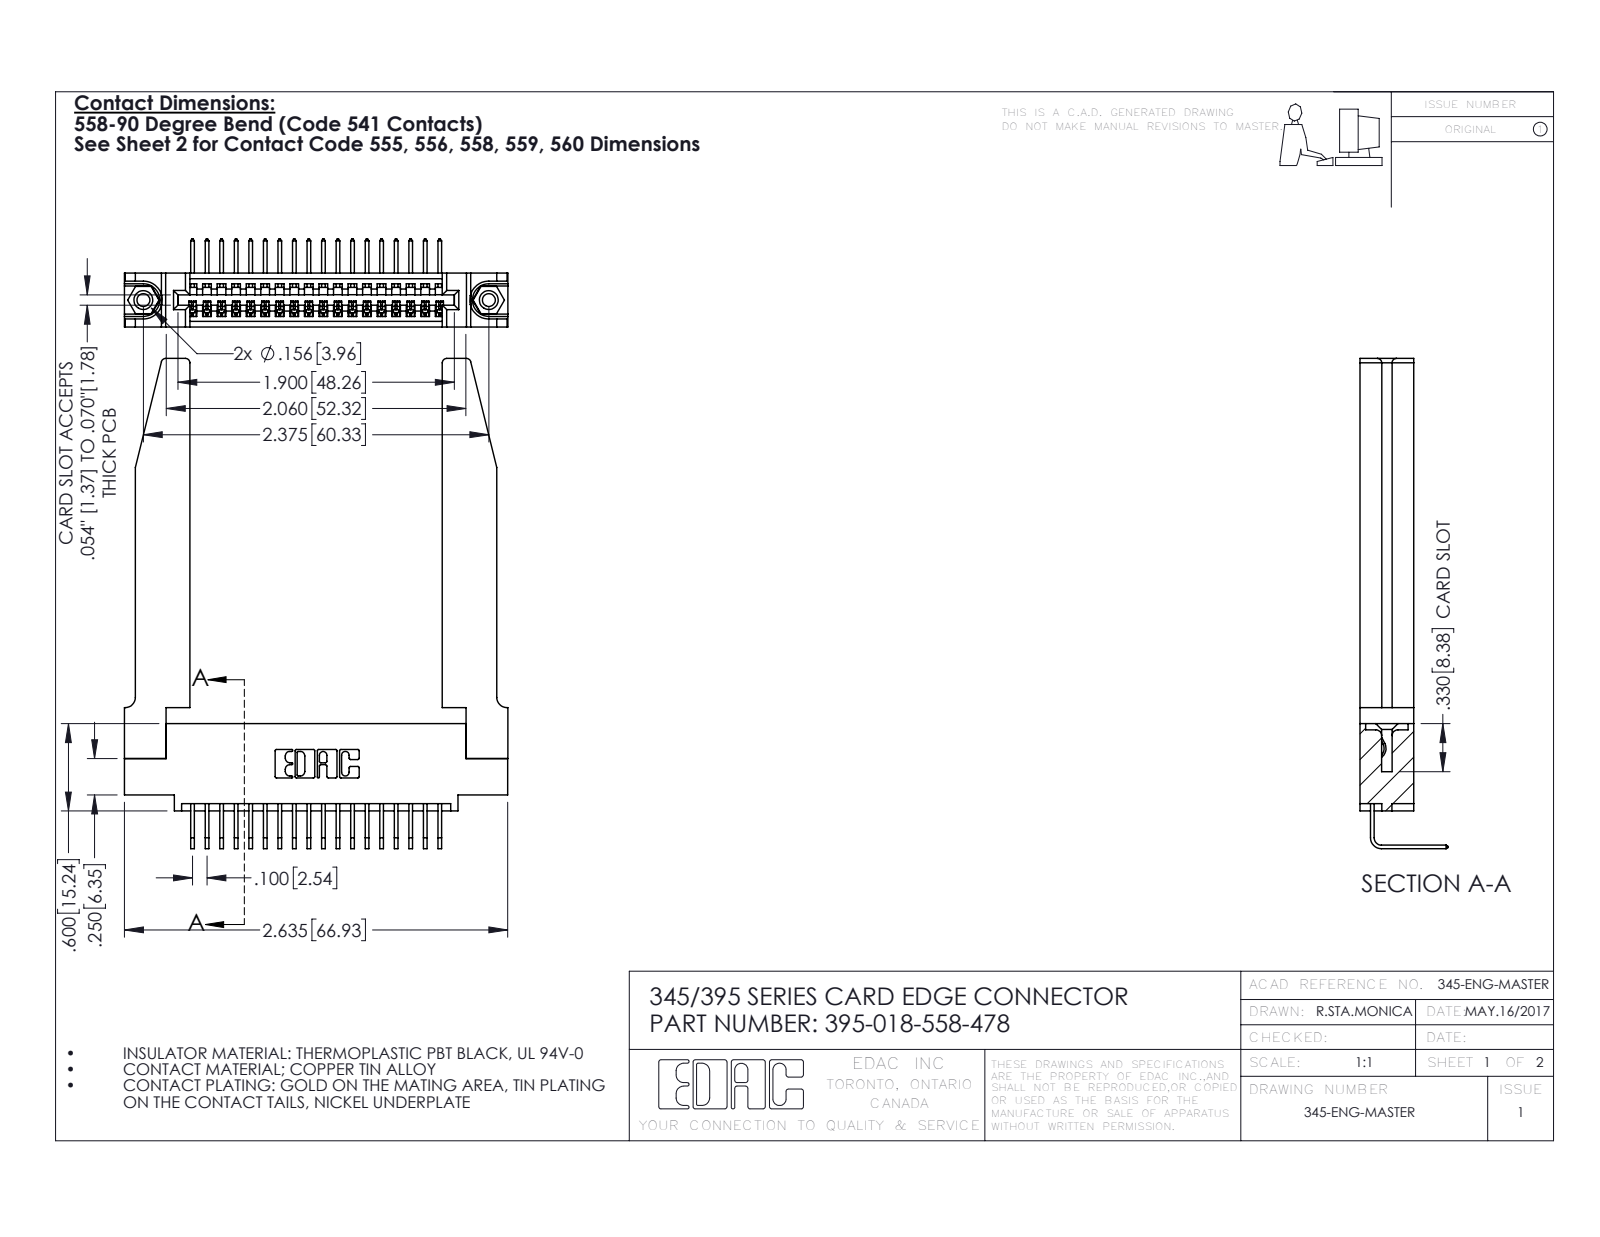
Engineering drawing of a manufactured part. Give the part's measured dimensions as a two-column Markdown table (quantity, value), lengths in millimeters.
| quantity | value |
| --- | --- |
| part name | 345-292-001_558 Tail - 2; 345-250-001_345-250-001-102; 395-018-558-478; 345 Part_0.110 Offset - 0.156 Dia-TH (+1 more) |
| STEP written by | SolidWorks 2016 (CONFIG_CONTROL_DESIGN) |
| units | millimeters |
| bodies | 23 solids, 1444 faces (982 planar, 410 cylindrical, 52 other) |
| overall size | 85.6 × 67 × 15.4 |
| volume | 13 900 mm³ |
| surface area | 15 120 mm² |
| round holes (diameter × count) | 2.3 × 2, 3.2 × 2, 4 × 2, 1.6 × 1 |
| round bosses / shafts (diameter × count) | 3.9 × 2 |
| partial cylindrical surfaces (radius × count) | 0.2 × 36, 0.3 × 22, 0.8 × 8, 0.2 × 6, 0.8 × 6, 0.7 × 3, 0.8 × 2, 1 × 2 |
| main face-to-face distances | 9.4, 1.8, 7.6, 3.8, 3.8, 5.1, 2.5, 6.9, 0.6, 5.6 |
| hole center spacings | 6.9, 54.4, 60.3 |
